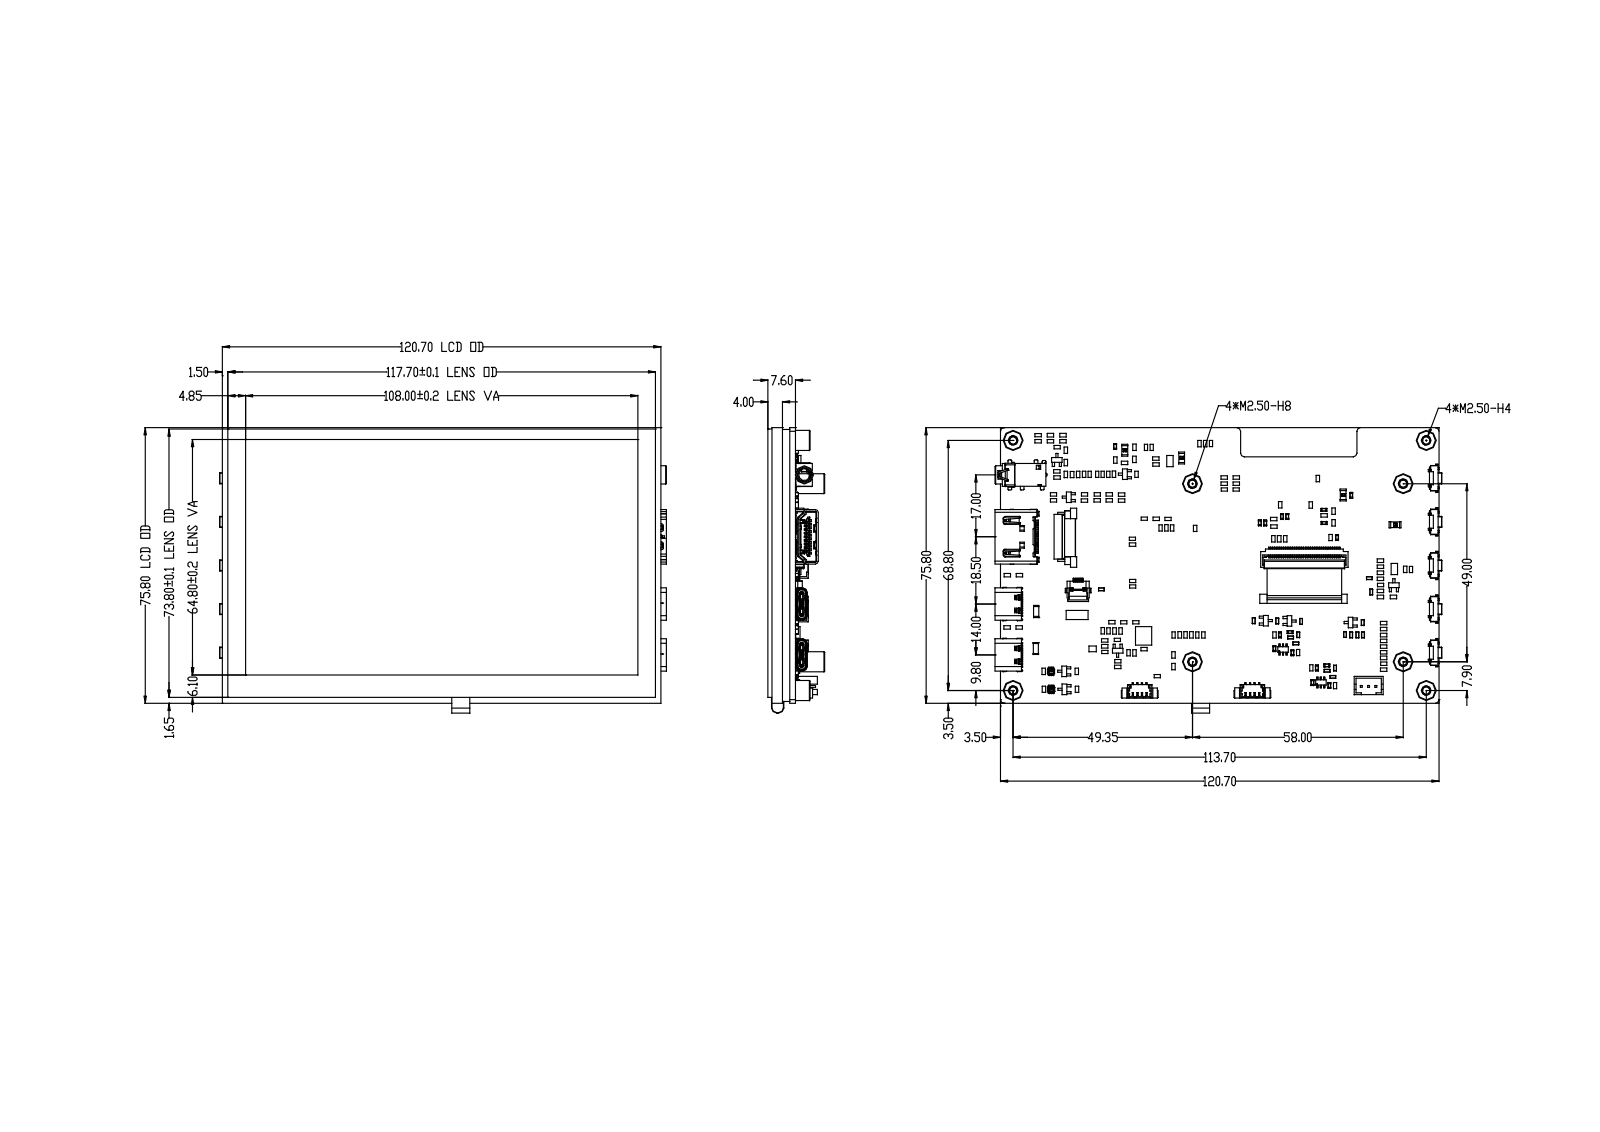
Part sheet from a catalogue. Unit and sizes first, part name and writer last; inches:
Units: inches
Overall size (bounding box): 4.843 × 3.091 × 0.614
Round holes (diameter × count): ⌀0.031 ×13, ⌀0.098 ×8, ⌀0.169 ×8, ⌀0.039 ×5, ⌀0.03 ×4, ⌀0.009 ×2, ⌀0.055 ×2, ⌀0.142 ×1
Round bosses / shafts (diameter × count): ⌀0.024 ×10, ⌀0.217 ×8, ⌀0.165 ×8, ⌀0.02 ×4, ⌀0.051 ×2, ⌀0.028 ×2, ⌀0.197 ×1
Partial cylindrical surfaces — rounded edges, fillets, slot ends (radius × count): R0.004 ×181, R0.008 ×74, R0.006 ×73, R0.01 ×63, R0.016 ×39, R0.012 ×38, R0.014 ×21, R0.02 ×19
Main face-to-face distances: 0.114, 0.079, 0.193, 0.256, 0.063, 0.142, 0.043, 0.297, 0.041, 0.112
Hole centre spacings: 0.091, 0.079, 0.116, 0.132, 0.15, 0.228, 0.246, 0.317
Volume: 3.491 in³ · Surface area: 115.3 in²
Bodies: 307 solids, 9696 faces (6823 planar, 2195 cylindrical, 678 other)
Part name (STEP PRODUCT): 5INCH-1024X600-LCD; 5DP-CAPLCD-TP_G; 5INCH-1024X600-LCD_TP_ASM; SMTSO-M2_5-4ET (+8 more)
STEP written by: CREO PARAMETRIC BY PTC INC, 2021063 (CONFIG_CONTROL_DESIGN)
